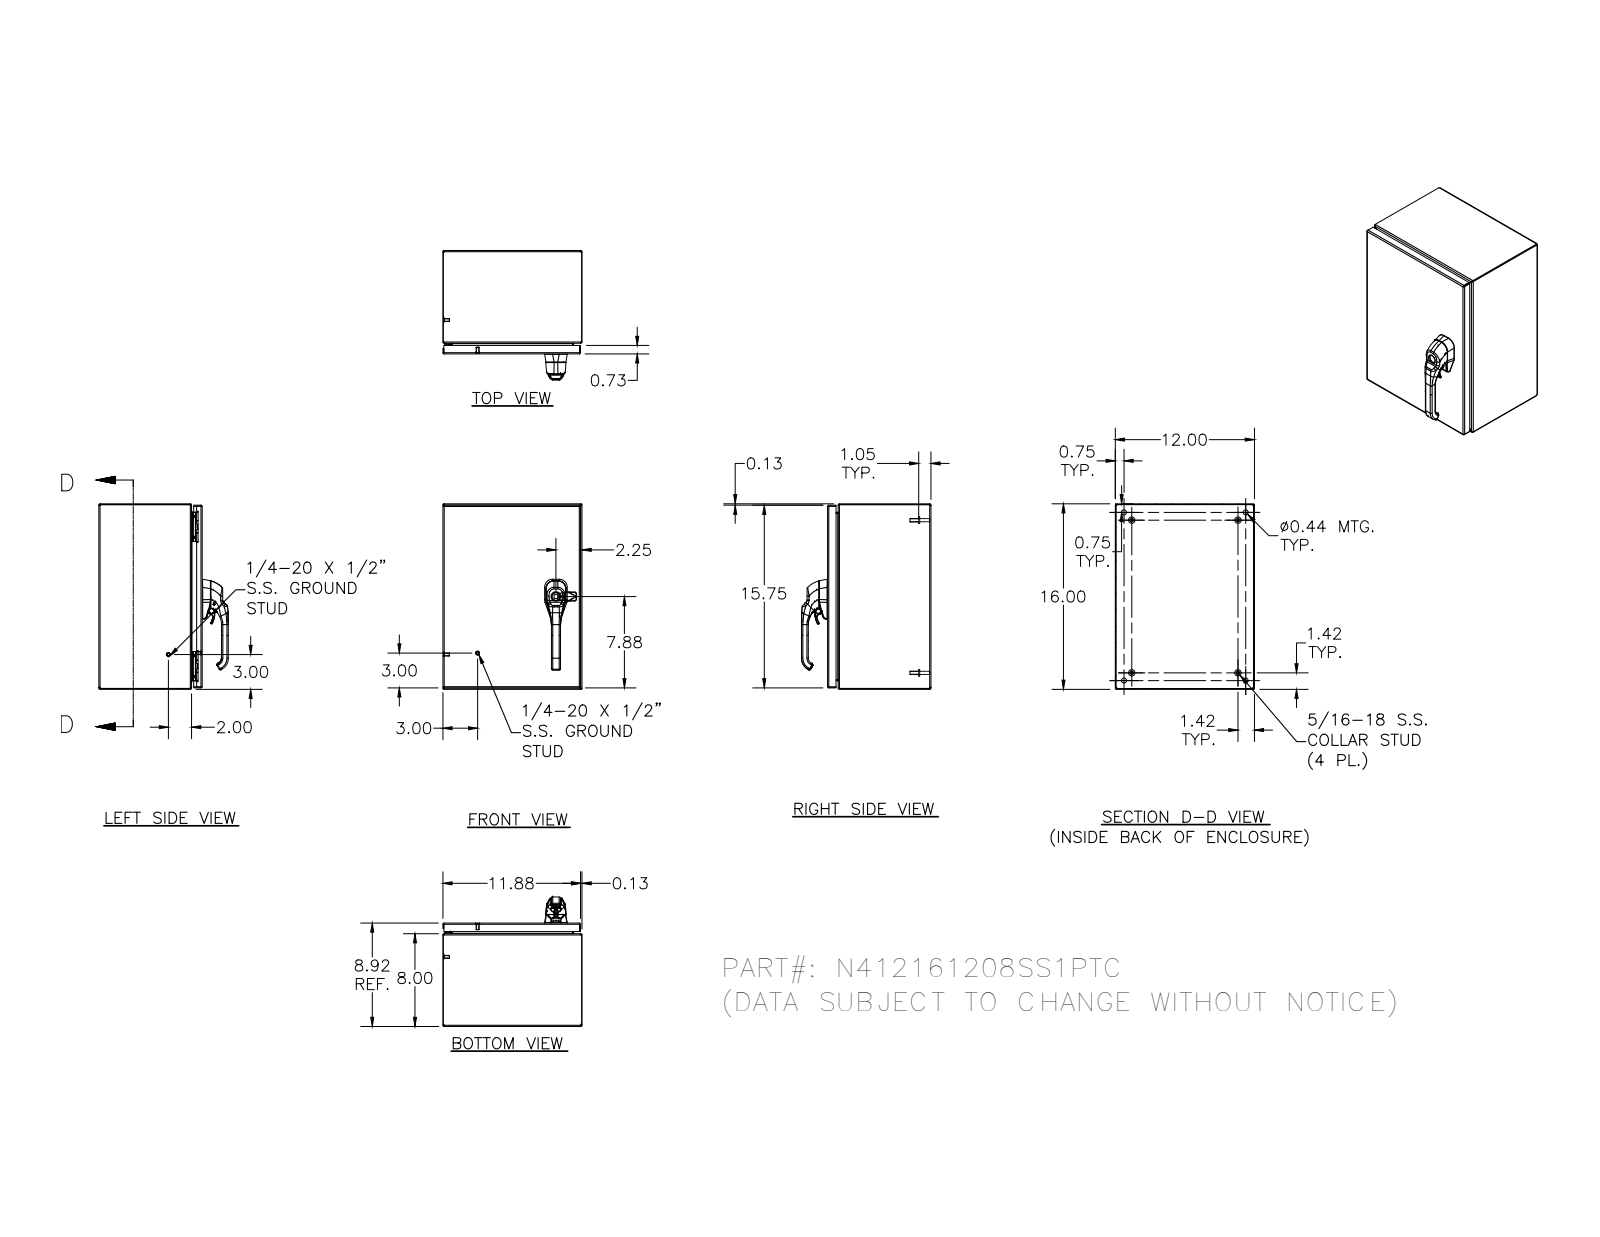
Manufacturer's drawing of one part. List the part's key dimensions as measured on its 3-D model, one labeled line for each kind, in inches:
Part name (STEP PRODUCT): N412161208SS1PTC; N412161208SS1PTCBKP; N4121612SS1PTCLID; HFW328176 (+8 more)
STEP written by: Autodesk Inventor 2012 (AUTOMOTIVE_DESIGN)
Units: inches
Bodies: 41 solids, 2782 faces (882 planar, 1035 cylindrical, 865 other)
Overall size (bounding box): 16 × 12 × 11.166
Volume: 77.43 in³ · Surface area: 2 009 in²
Round holes (diameter × count): ⌀0.093 ×4, ⌀0.152 ×4, ⌀0.167 ×4, ⌀0.172 ×4, ⌀0.188 ×4, ⌀0.437 ×4, ⌀0.213 ×3, ⌀0.281 ×3, ⌀0.156 ×2, ⌀0.315 ×2, ⌀0.402 ×2, ⌀0.413 ×2
Round bosses / shafts (diameter × count): ⌀0.25 ×10, ⌀0.563 ×4, ⌀0.36 ×4, ⌀0.32 ×4, ⌀0.3 ×4, ⌀0.275 ×4, ⌀0.256 ×4, ⌀0.164 ×4
Partial cylindrical surfaces — rounded edges, fillets, slot ends (radius × count): R0.02 ×173, R0.012 ×101, R0.031 ×30, R0.05 ×26, R0.019 ×21, R0.105 ×20, R0.016 ×18, R0.079 ×14
Main face-to-face distances: 0.074, 8.843, 11.926, 15.926, 8.917, 8.769, 12, 11.852, 16, 15.852
Hole centre spacings: 11.996, 0.017, 0.66, 12.656, 0.019, 0.5, 0.648, 0.656
